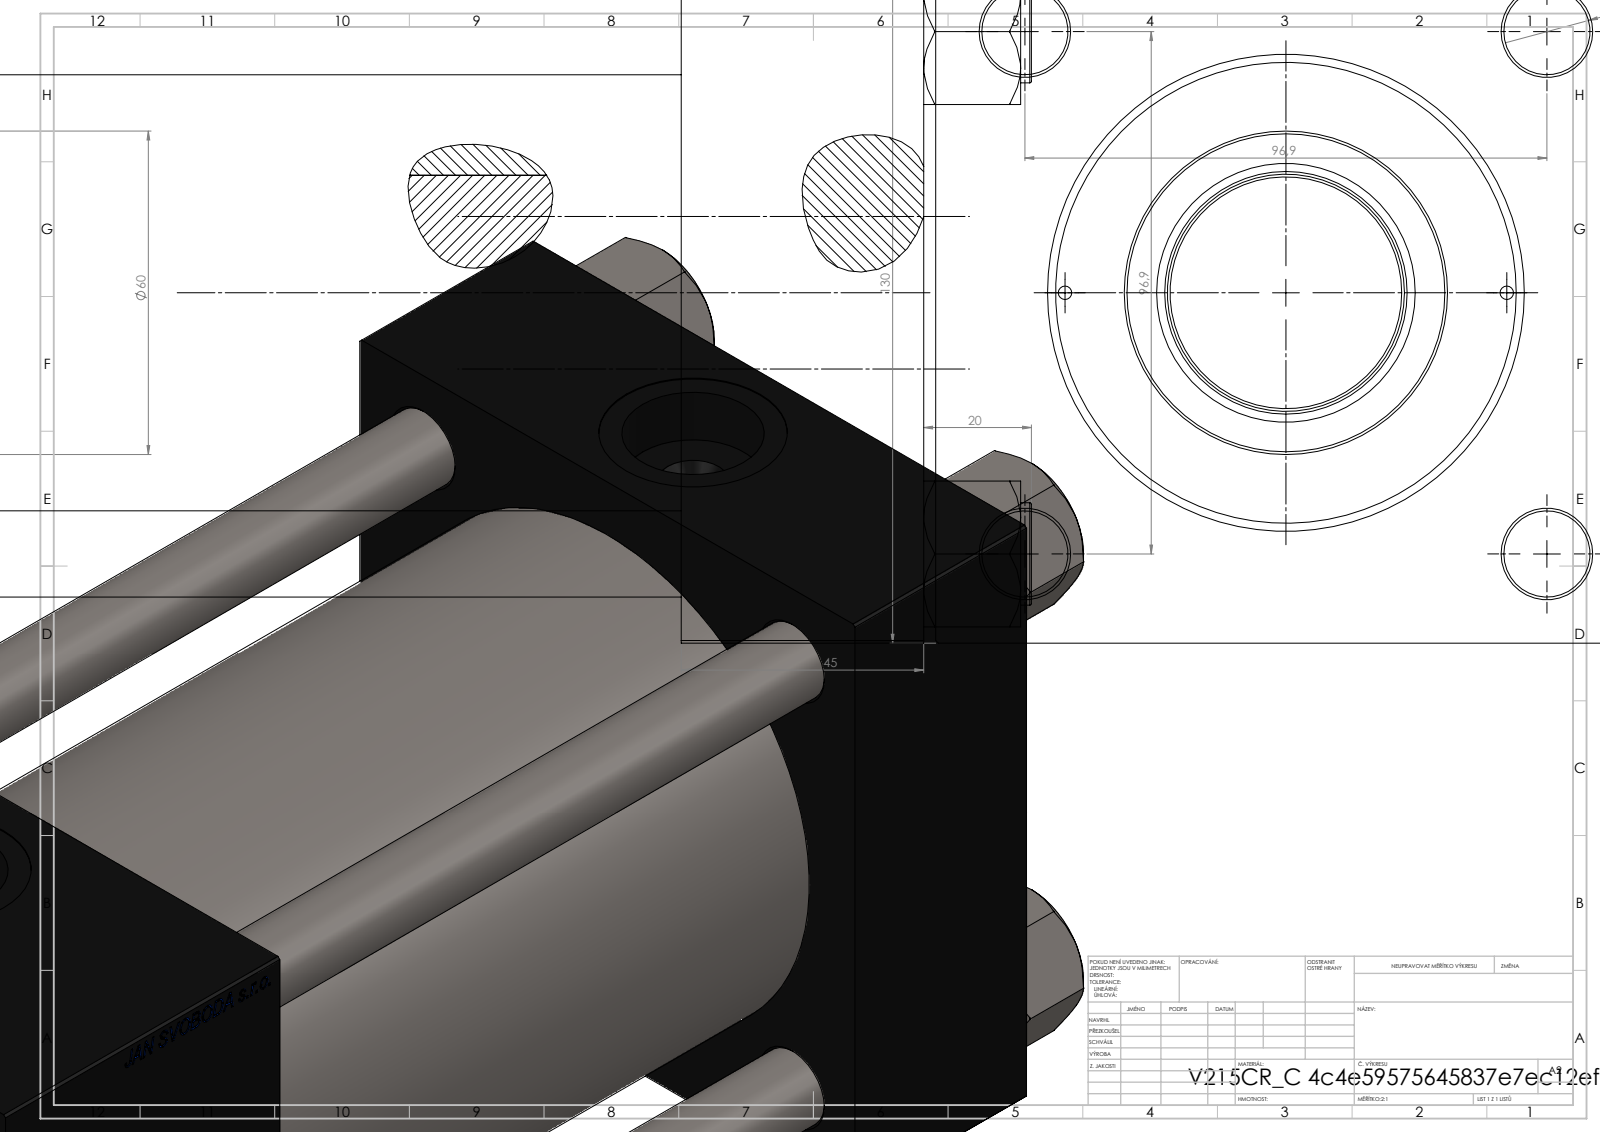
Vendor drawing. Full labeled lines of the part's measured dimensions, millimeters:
Part name (STEP PRODUCT): V215CR_ROD_END_F; V215_VC_A; NUT_M5_C; V215CR_C_Body (+2 more)
STEP written by: SolidWorks 2019 (CONFIG_CONTROL_DESIGN)
Units: millimetres
Bodies: 12 solids, 1216 faces (579 planar, 95 cylindrical, 542 other)
Overall size (bounding box): 367 × 130 × 130
Volume: 2 746 000 mm³ · Surface area: 414 022 mm²
Round holes (diameter × count): ⌀16 ×4, ⌀2.5 ×2, ⌀7 ×2, ⌀26.44 ×2, ⌀35 ×2, ⌀31.5 ×1, ⌀45 ×1, ⌀48 ×1, ⌀76 ×1, ⌀85.5 ×1, ⌀100 ×1
Round bosses / shafts (diameter × count): ⌀19 ×4, ⌀106 ×1, ⌀60 ×1, ⌀44 ×1, ⌀33 ×1
Main face-to-face distances: 130, 45, 268, 223, 151, 196, 72, 96, 51, 100
Hole centre spacings: 49.02, 68.52, 96.9, 101.73, 41, 137.04, 82, 198.5
